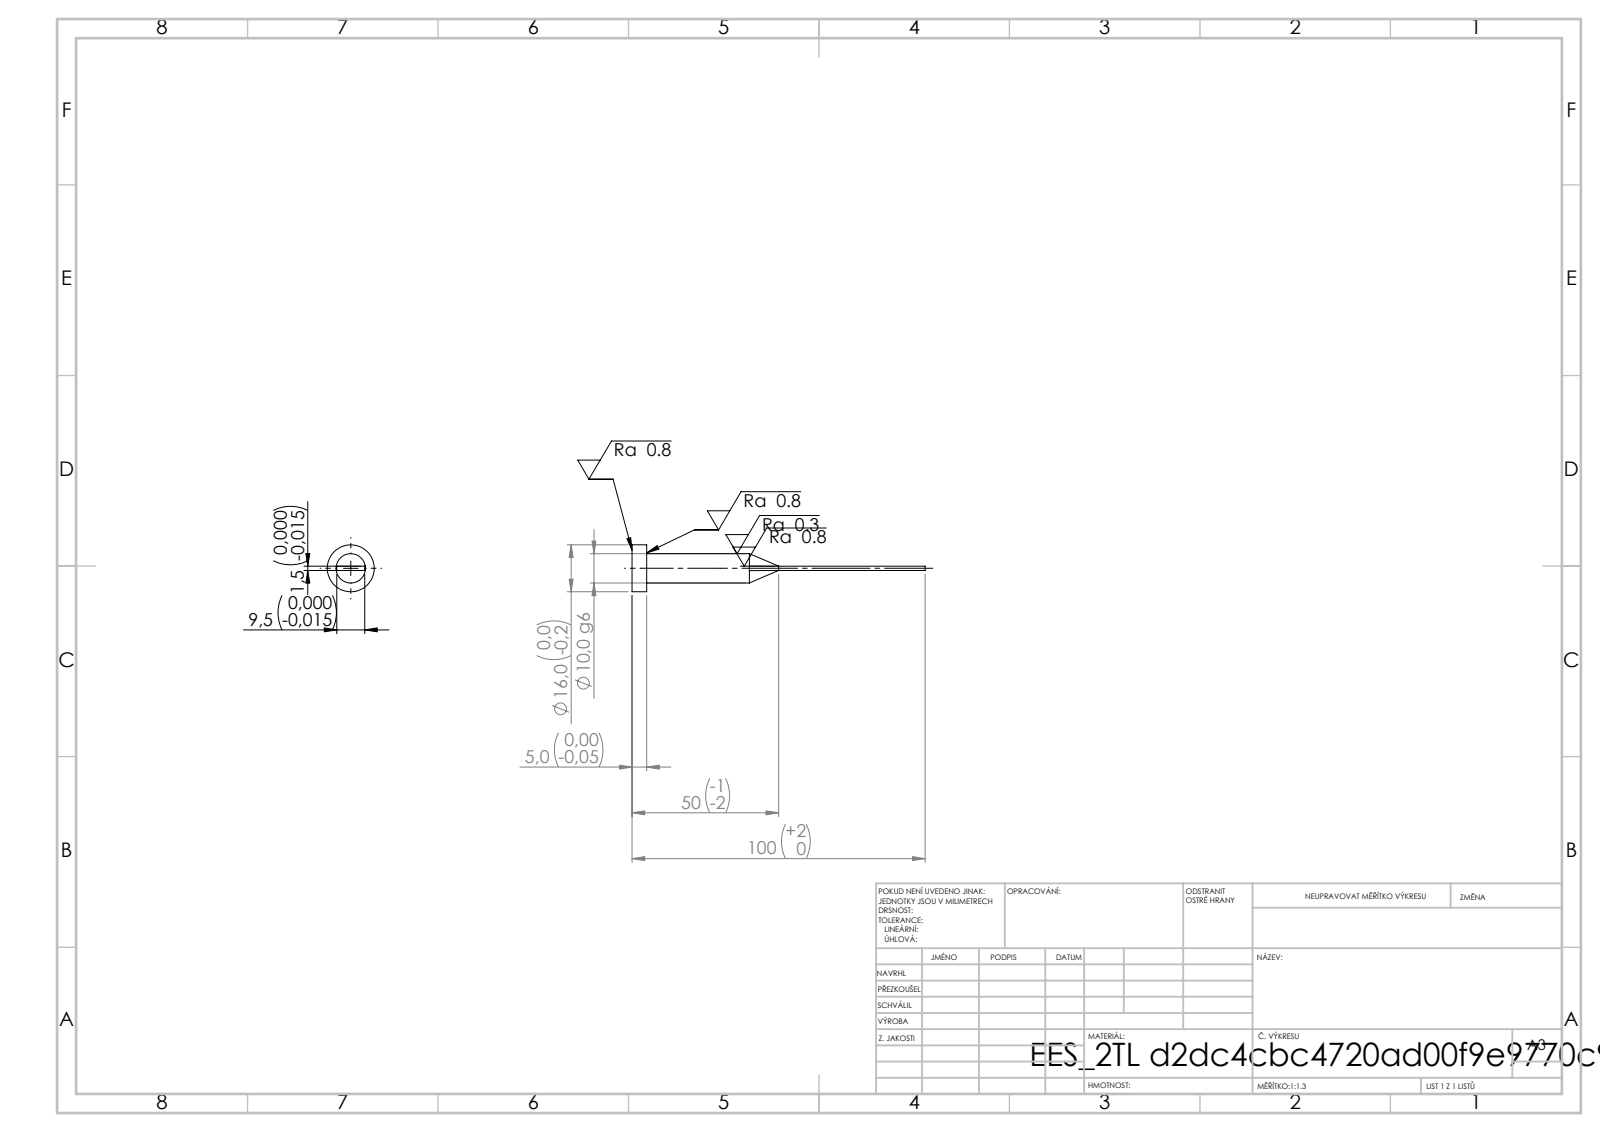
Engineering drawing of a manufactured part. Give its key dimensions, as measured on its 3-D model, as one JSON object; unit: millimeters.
{"step_written_by": "SolidWorks 2019 (CONFIG_CONTROL_DESIGN)", "units": "millimeters", "bodies": {"solids": 1, "faces": 15, "planar": 7, "cylindrical": 4, "other": 4}, "overall_size": [100, 16, 16], "volume_mm3": 4905, "surface_area_mm2": 3053, "round_bosses_or_shafts": [[16, 1], [10, 1]], "face_to_face_distances": [1.5, 5, 9.5, 100, 95]}
